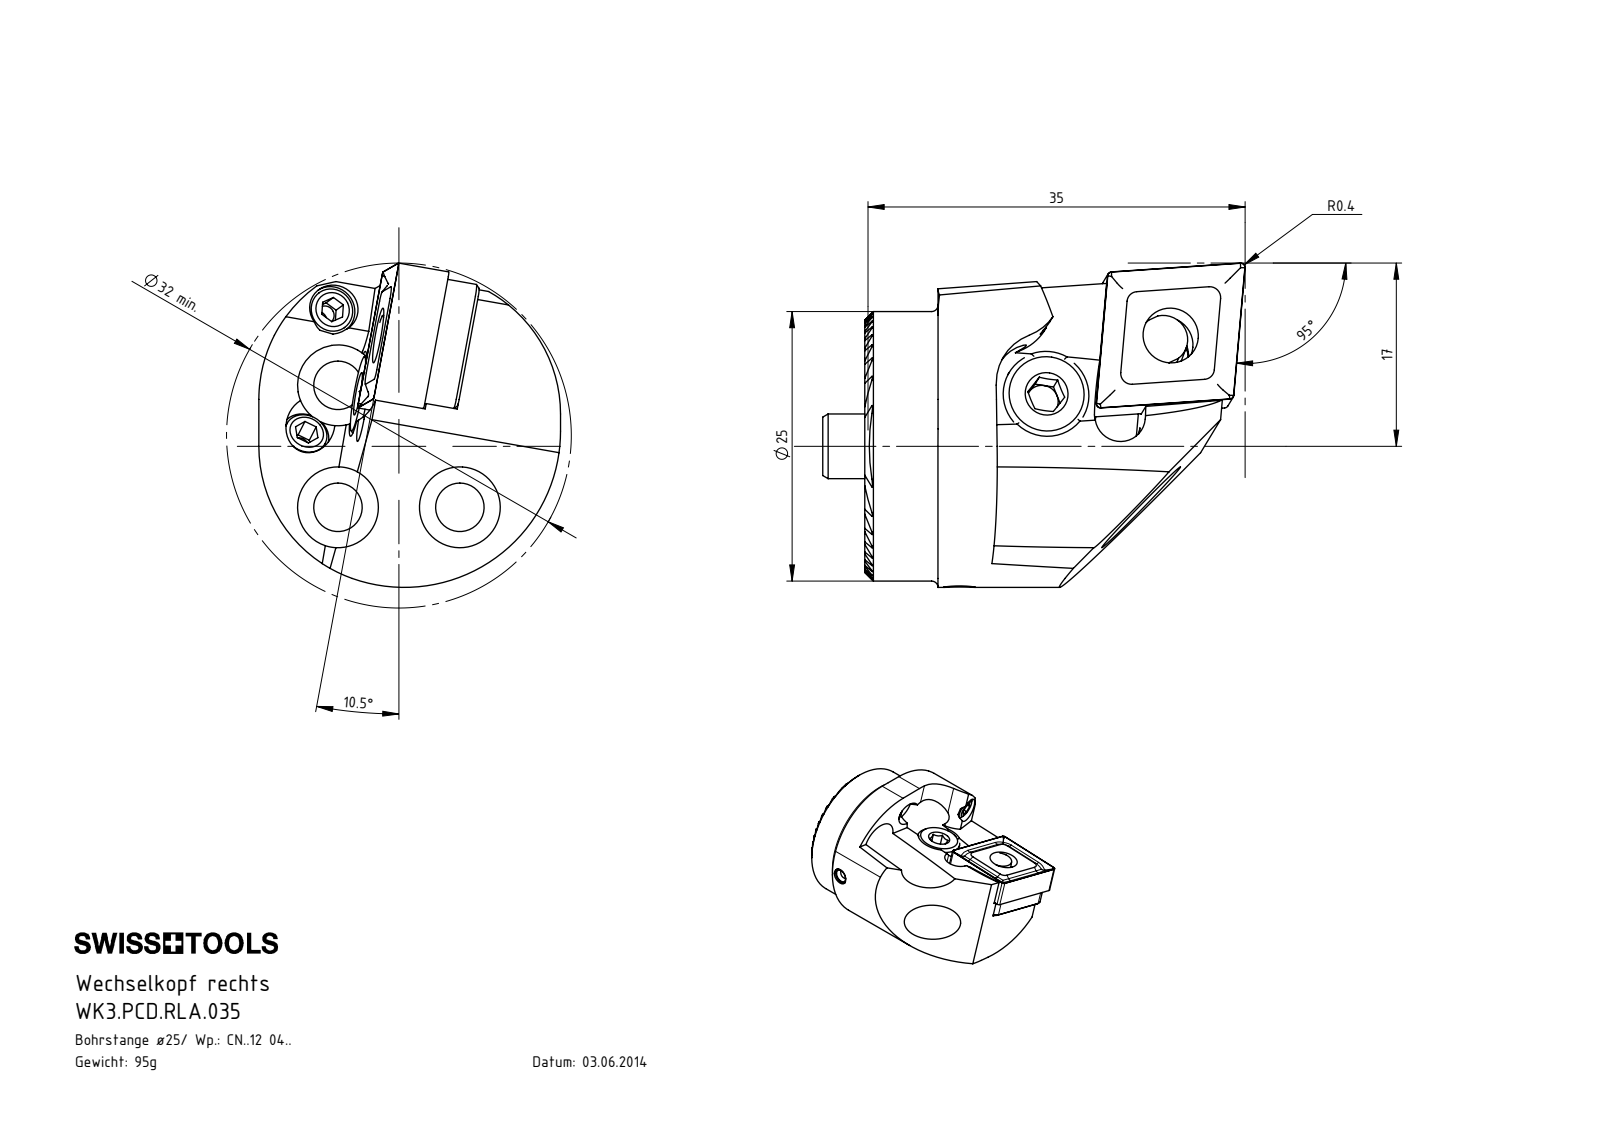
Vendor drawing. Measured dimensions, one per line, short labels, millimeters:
name: KVT_MB_600_030; CNMG120404; WK3.PCD.RLA.035; WK3-PCD.RLA.035_B (+6 more)
written by: SolidWorks 2017 (AUTOMOTIVE_DESIGN)
unit: mm
bodies: 15 solids, 612 faces (223 planar, 199 cylindrical, 190 other)
size: 39.2 × 30.09 × 28
volume: 11 348 mm³; area: 8 886 mm²
holes: 5× ⌀4.5, 3× ⌀2.38, 3× ⌀2.5, 3× ⌀7.5, 2× ⌀1.7, 2× ⌀3, 2× ⌀3.3, 1× ⌀4.2, 1× ⌀5.16, 1× ⌀6, 1× ⌀6.4, 1× ⌀7
bosses: 3× ⌀3, 2× ⌀4, 1× ⌀25, 1× ⌀8, 1× ⌀7.9, 1× ⌀6.4, 1× ⌀4.5, 1× ⌀3.55
rounds: 20× R0.12, 4× R0.4, 4× R1, 3× R13, 2× R2.5, 2× R3.2, 2× R5, 1× R2.1
face distances: 4.33, 1.08, 3.25, 5.41, 8.66, 7.58, 2.16, 2.17, 3.18, 9.74
hole spacings: 8, 11.32, 12.8, 12.85, 16.01
